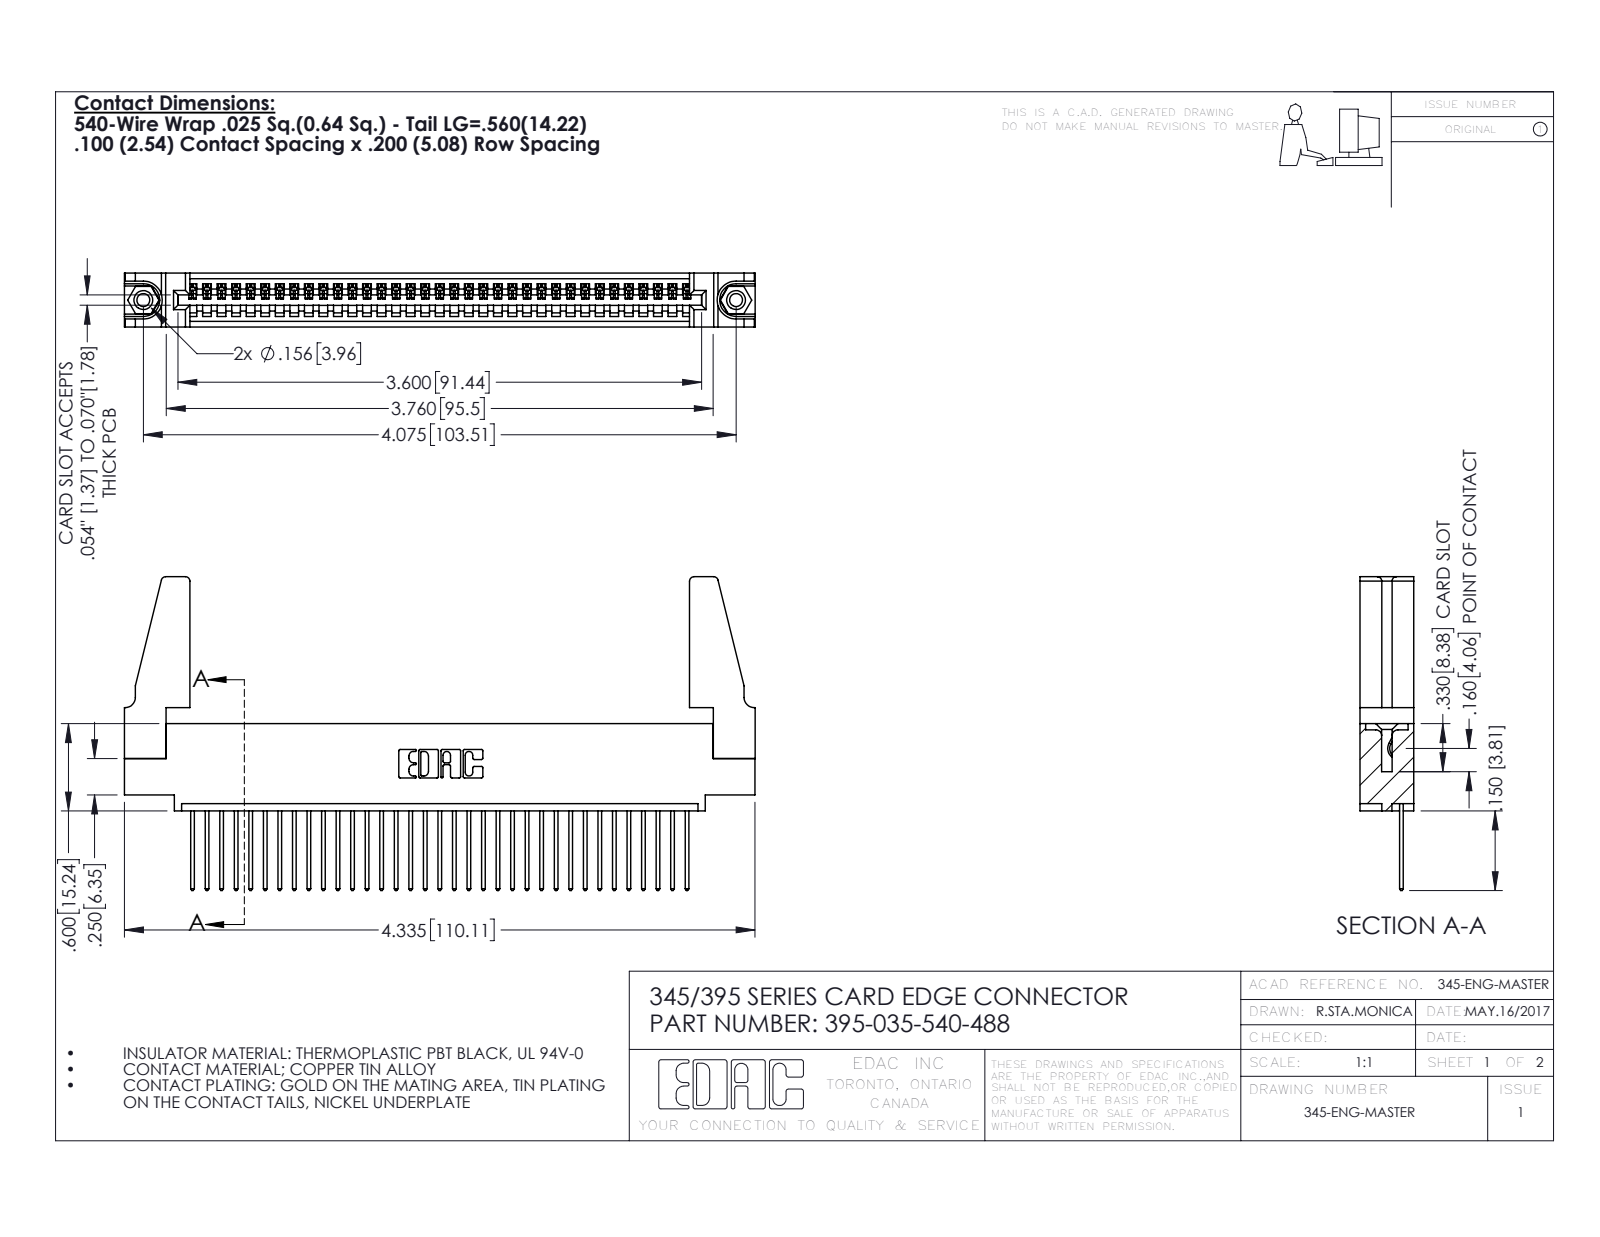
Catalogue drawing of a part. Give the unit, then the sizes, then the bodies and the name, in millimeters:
Units: millimetres
Overall size (bounding box): 110.1 × 54.8 × 9.4
Round holes (diameter × count): ⌀2.3 ×2, ⌀3.2 ×2, ⌀4 ×2, ⌀1.6 ×1
Round bosses / shafts (diameter × count): ⌀3.9 ×2
Partial cylindrical surfaces — rounded edges, fillets, slot ends (radius × count): R0.2 ×70, R0.3 ×70, R0.3 ×22, R0.8 ×8, R0.2 ×6, R0.8 ×6, R0.7 ×3, R0.8 ×2
Main face-to-face distances: 1.8, 7.6, 9.4, 2.5, 6.9, 0.6, 5.1, 5.7, 3.8, 1.8
Hole centre spacings: 6.9, 97.5, 103.5
Volume: 13 600 mm³ · Surface area: 17 250 mm²
Bodies: 40 solids, 2284 faces (1556 planar, 712 cylindrical, 16 other)
Part name (STEP PRODUCT): 345 Part_0.110 Offset - 0.156 Dia-TH; 345-220-078_345-220-088; 345-292-001_345-293-140; 345-250-001_345-250-001-102 (+1 more)
STEP written by: SolidWorks 2016 (CONFIG_CONTROL_DESIGN)
